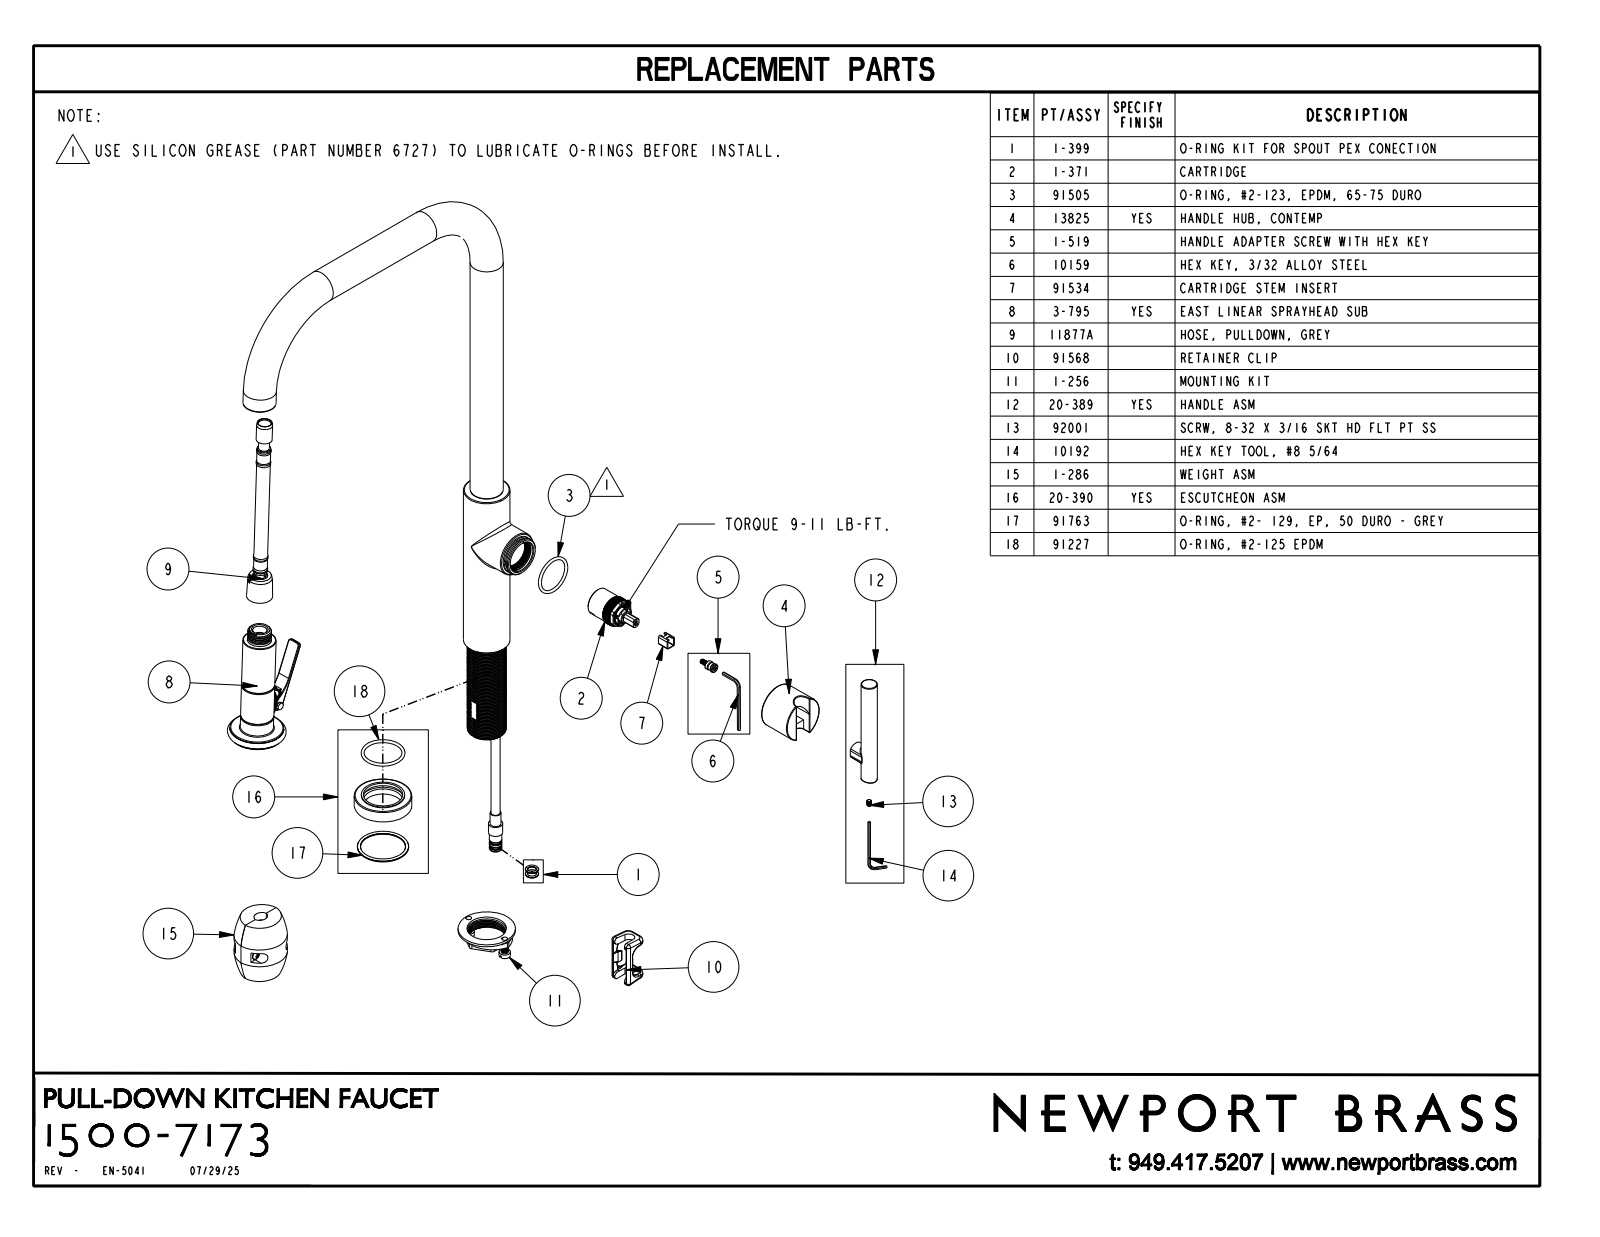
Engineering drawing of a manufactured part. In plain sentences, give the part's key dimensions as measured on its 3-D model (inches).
The part is named "1500-7173_SW0004". Its 3-D file was written by "CREO PARAMETRIC BY PTC INC, 2025093 (CONFIG_CONTROL_DESIGN)". It is 4 solids with 471 faces: 87 planar, 179 cylindrical and 205 other. Overall it measures 19.87 by 13.178 by 4.027 inches. Its volume is 48.35 cubic inches and its surface area 175.6 square inches. Round holes: 1 of diameter 0.21, 1 of diameter 0.228, 1 of diameter 1.035. Round bosses or shafts: 18 of diameter 0.102, 2 of diameter 1.14, 1 of diameter 1.98, 1 of diameter 1.855, 1 of diameter 1.6, 1 of diameter 1.58, 1 of diameter 1.354, 1 of diameter 1.142. Partial cylindrical surfaces (rounded edges, fillets, slot ends): 32 of radius 0.02, 23 of radius 0.03, 17 of radius 0.06, 5 of radius 0.025, 4 of radius 0.045, 4 of radius 0.12, 3 of radius 0.1, 3 of radius 0.313. The main face-to-face distances are 6.735, 0.308, 0.025, 3.959, 3.651, 6.755, 0.02, 3.933, 3.626, 0.425.
